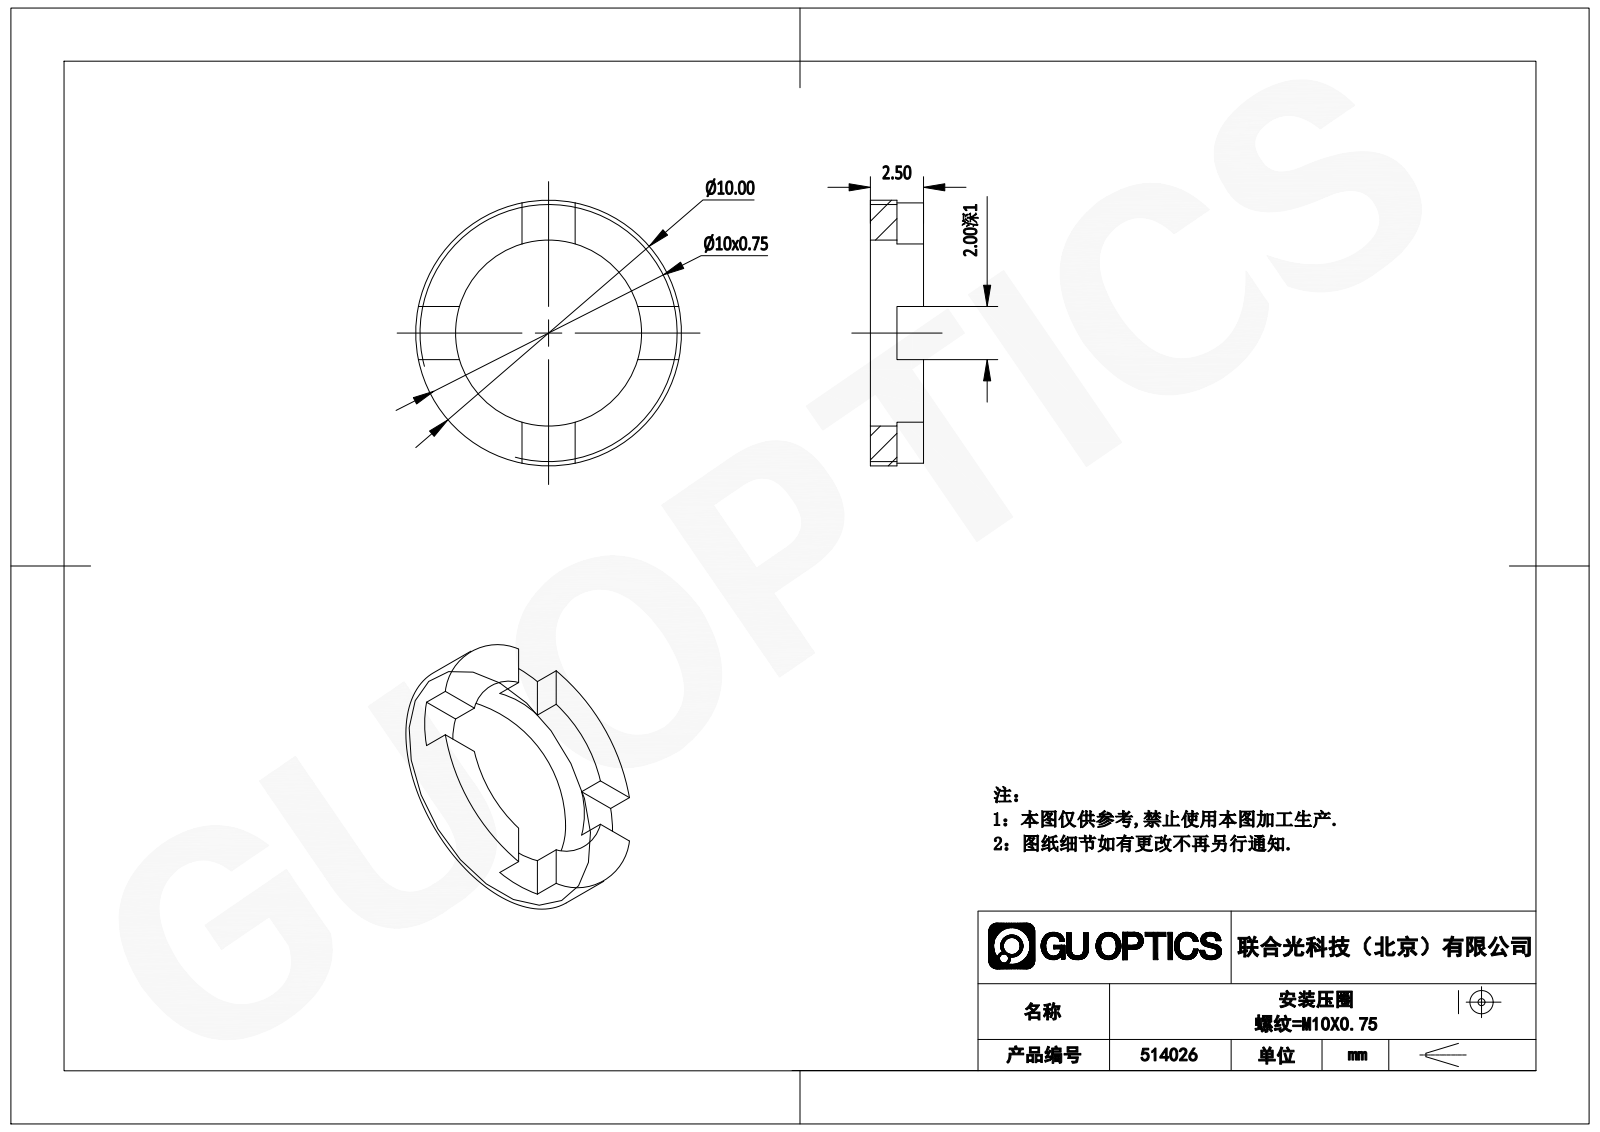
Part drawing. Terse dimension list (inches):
name: 514026
written by: SolidWorks 2020 (CONFIG_CONTROL_DESIGN)
unit: in
bodies: 1 solid, 21 faces (17 planar, 4 cylindrical, 0 other)
size: 0.394 × 0.394 × 0.098
volume: 0.005 in³; area: 0.326 in²
holes: 1× ⌀0.276
bosses: 1× ⌀0.394
face distances: 0.098, 0.059, 0.039, 0.079
